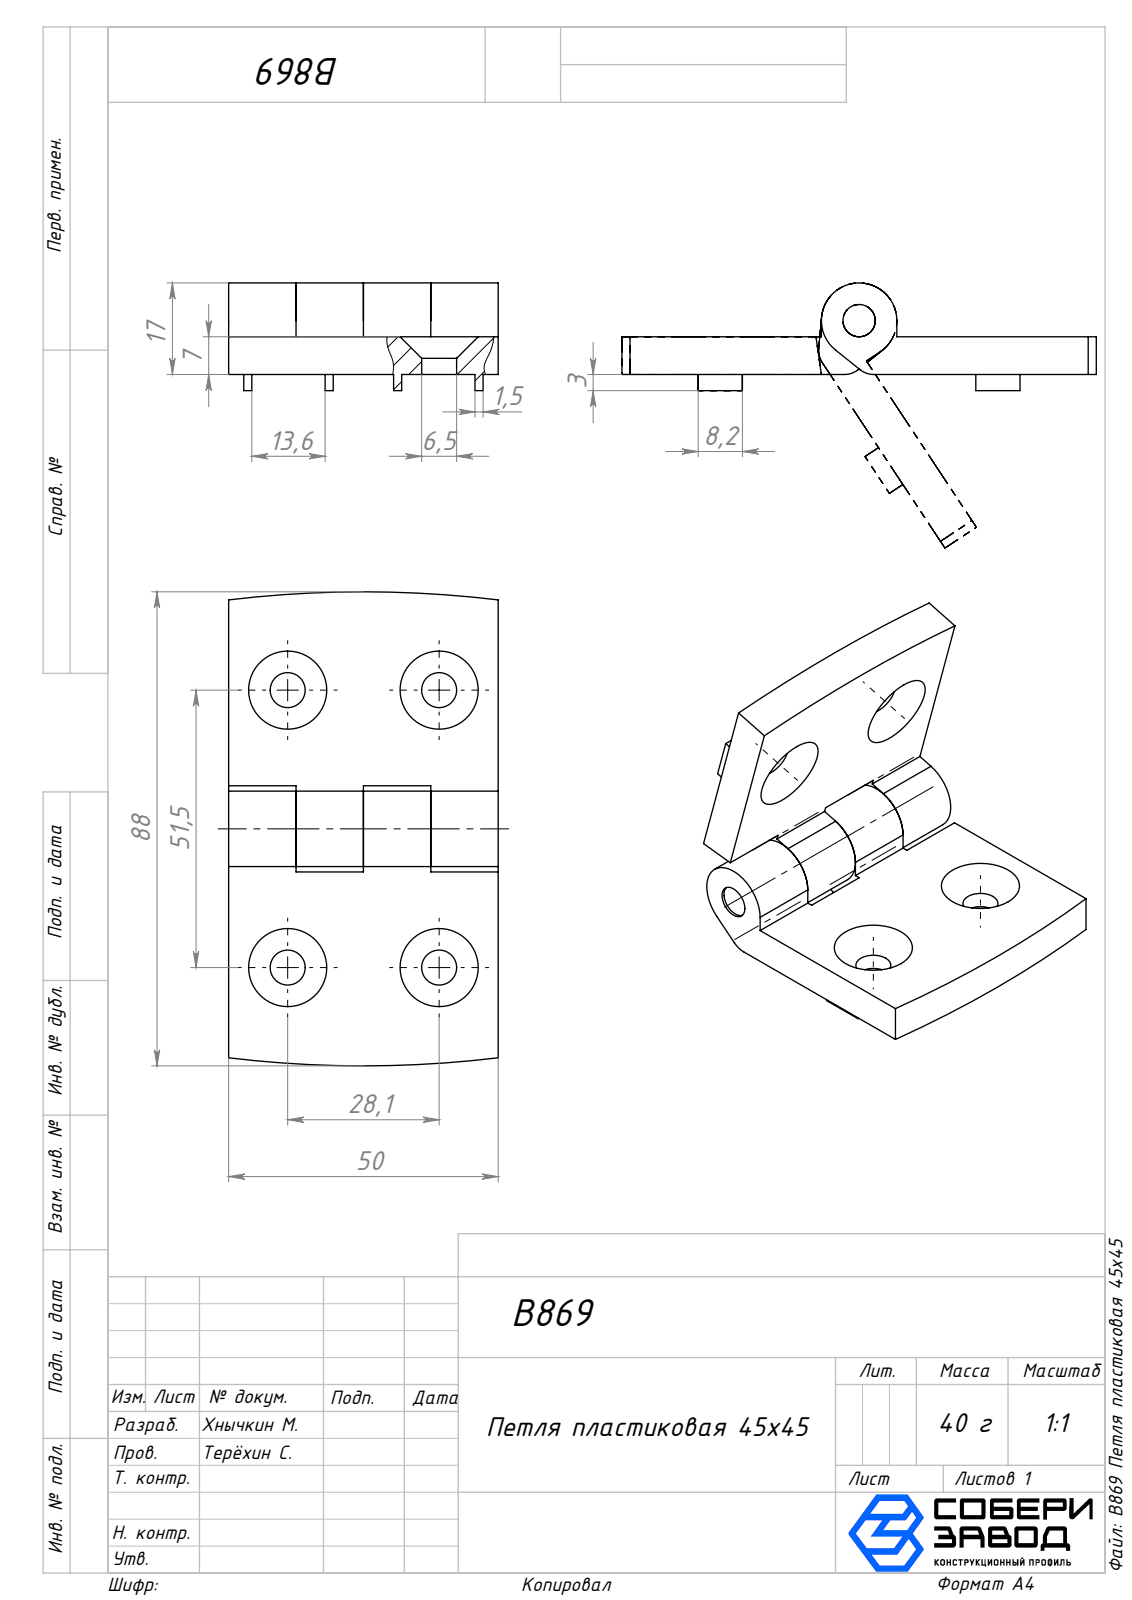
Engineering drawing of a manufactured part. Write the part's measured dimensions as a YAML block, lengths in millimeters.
part_name: "Палец_00; B869 Петля пластиковая 45х45; Петля 45_00"
step_written_by: "SolidWorks 2025 (AUTOMOTIVE_DESIGN)"
units: millimeters
bodies: {solids: 3, faces: 108, planar: 68, cylindrical: 32, other: 8}
overall_size: [88, 50, 20]
volume: 33133
surface_area: 15328
round_holes:
  - {diameter: 6.5, count: 4}
  - {diameter: 6, count: 1}
partial_cylinders:
  - {radius: 4, count: 2}
  - {radius: 209.08, count: 2}
  - {radius: 7, count: 1}
face_to_face_distances: [7, 12.5, 25, 50, 37.5, 1.5, 15.1, 27.8, 8.2, 7.1]
hole_center_spacings: [28.1, 51.5, 58.67]
